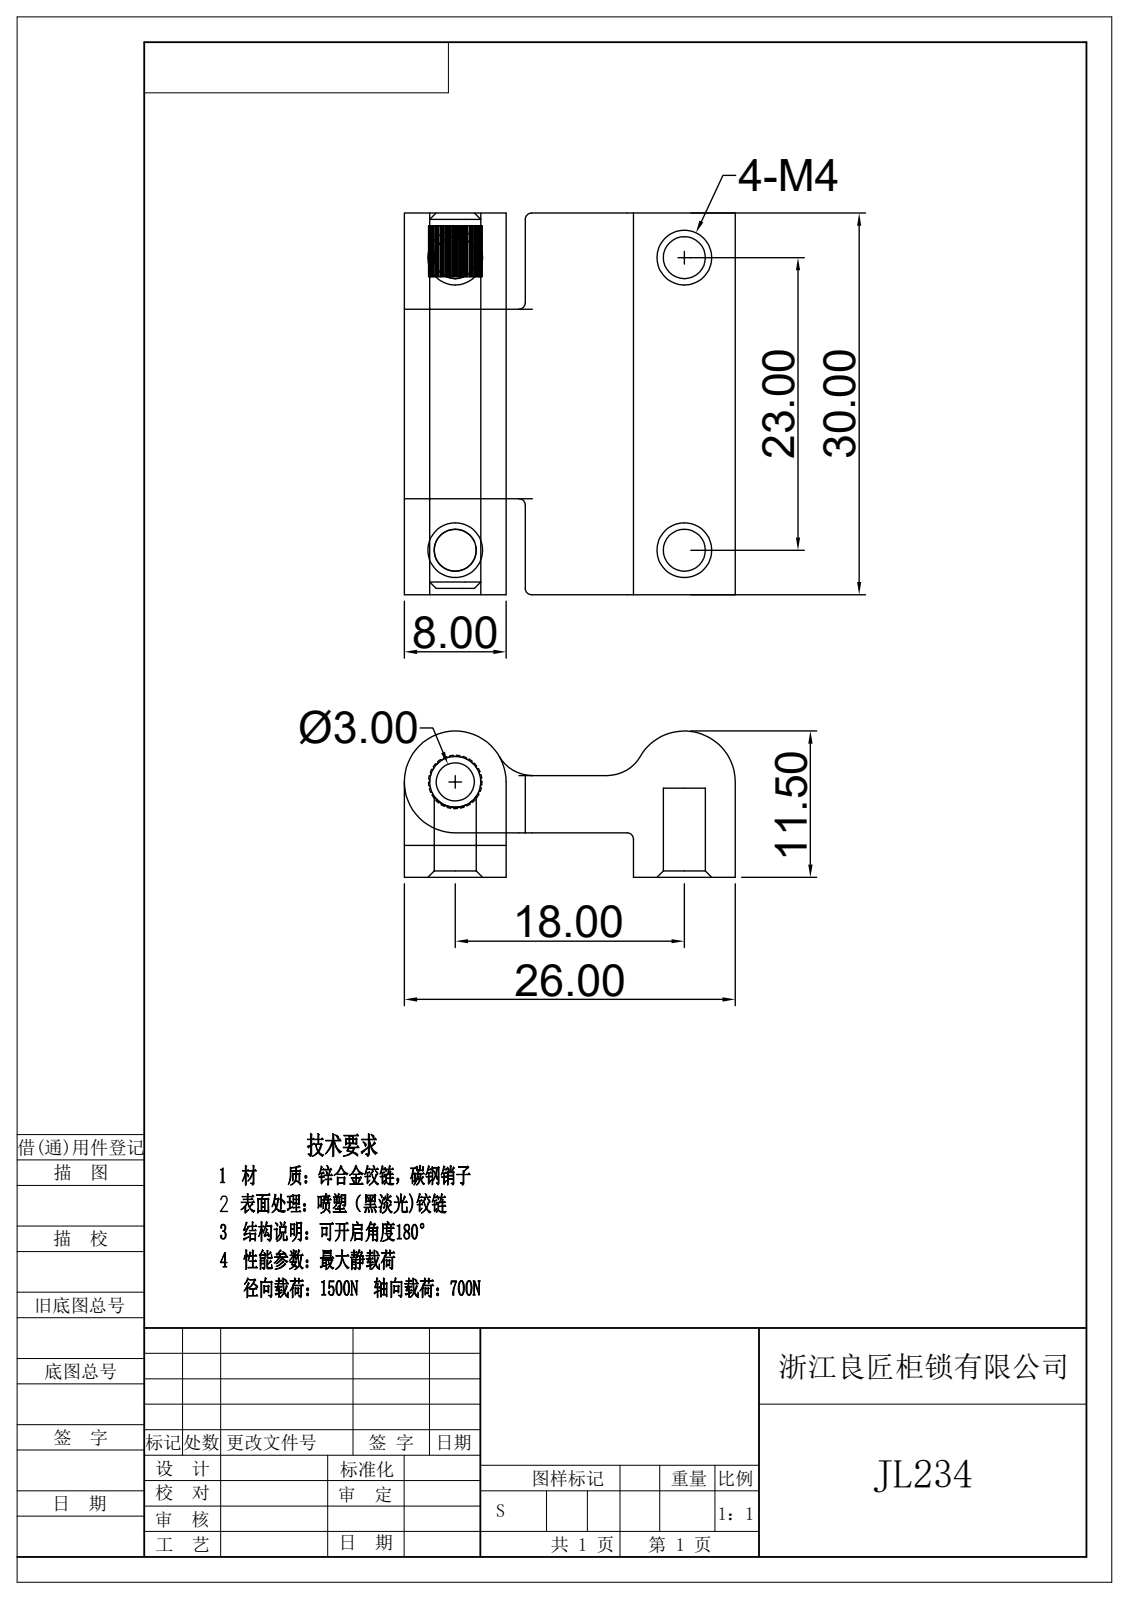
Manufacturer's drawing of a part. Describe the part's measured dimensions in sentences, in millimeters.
The part is named "CL234; CL234 Female Hinge; CL234 Male Hinge". Its 3-D file was written by "Rhino 8.5 (CONFIG_CONTROL_DESIGN)". It is 3 solids with 188 faces: 123 planar, 53 cylindrical and 12 other. Overall it measures 160.28 by 81.26 by 30 millimeters. Its volume is 5 989 cubic millimeters and its surface area 4 297 square millimeters. Round holes: 4 of diameter 3.3, 1 of diameter 4. Partial cylindrical surfaces (rounded edges, fillets, slot ends): 5 of radius 0.5, 2 of radius 3, 2 of radius 4, 1 of radius 2.1. The main face-to-face distances are 8, 3.5, 18, 4.5, 7.55, 22.45, 30, 26, 1, 2.5. The hole center spacings are 18, 23, 29.21.
